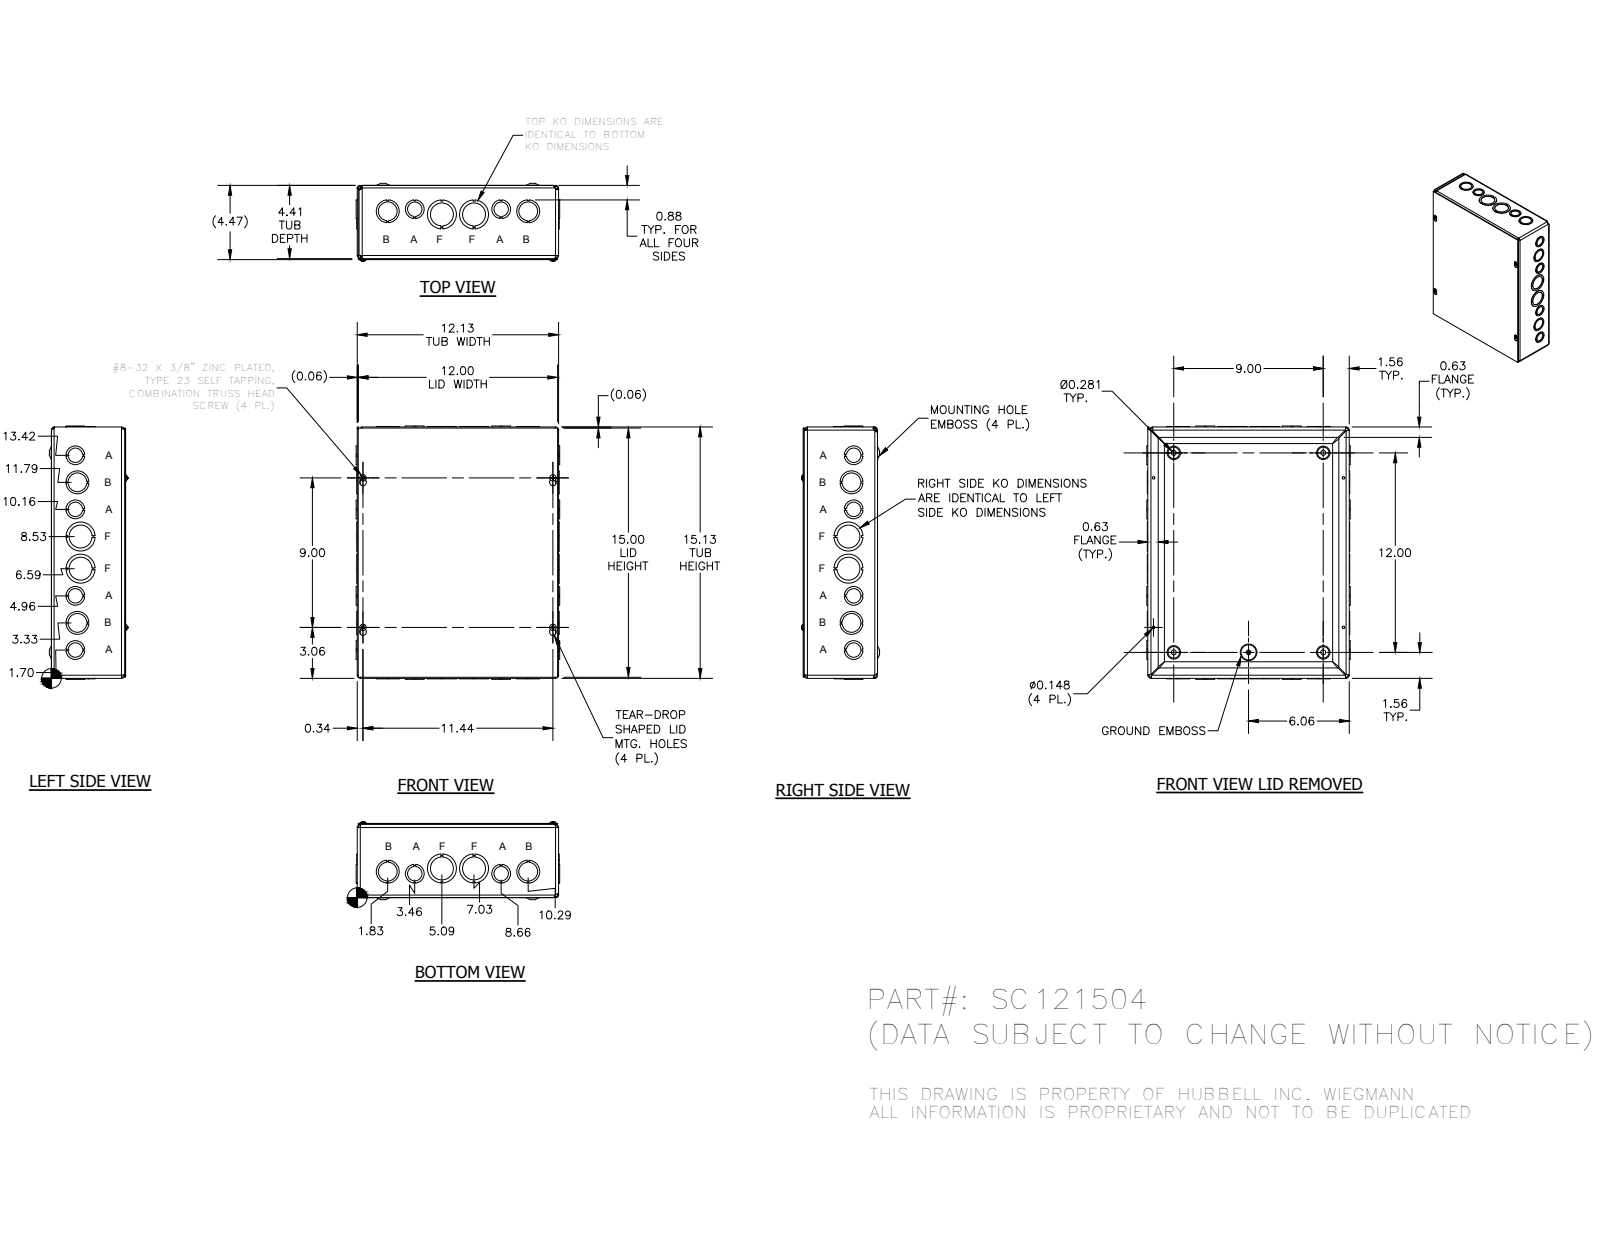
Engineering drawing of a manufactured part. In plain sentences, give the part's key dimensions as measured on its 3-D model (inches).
The part is named "SC1215BKP; SC121504WRA; SC1215LID; 34056 (+1 more)". Its 3-D file was written by "Autodesk Inventor 2014 (AUTOMOTIVE_DESIGN)". It is 30 solids with 1142 faces: 749 planar, 235 cylindrical and 158 other. Overall it measures 15.249 by 12.249 by 4.693 inches. Round holes: 10 of diameter 1.125, 8 of diameter 1.375, 6 of diameter 0.875, 4 of diameter 0.148, 4 of diameter 0.3, 4 of diameter 1.75, 1 of diameter 0.165. Round bosses or shafts: 4 of diameter 0.384, 4 of diameter 0.164, 1 of diameter 0.228. Partial cylindrical surfaces (rounded edges, fillets, slot ends): 12 of radius 0.125, 8 of radius 0.187, 4 of radius 0.055, 4 of radius 0.062, 4 of radius 0.094, 4 of radius 0.117, 4 of radius 0.124, 4 of radius 0.156. The main face-to-face distances are 0.062, 4.343, 4.405, 0.063, 4.406, 4.468, 15.063, 0.062, 12.125, 12.063. The hole center spacings are 1.635, 1.659, 1.933, 3.265, 3.584, 5.204, 6.831, 9.
